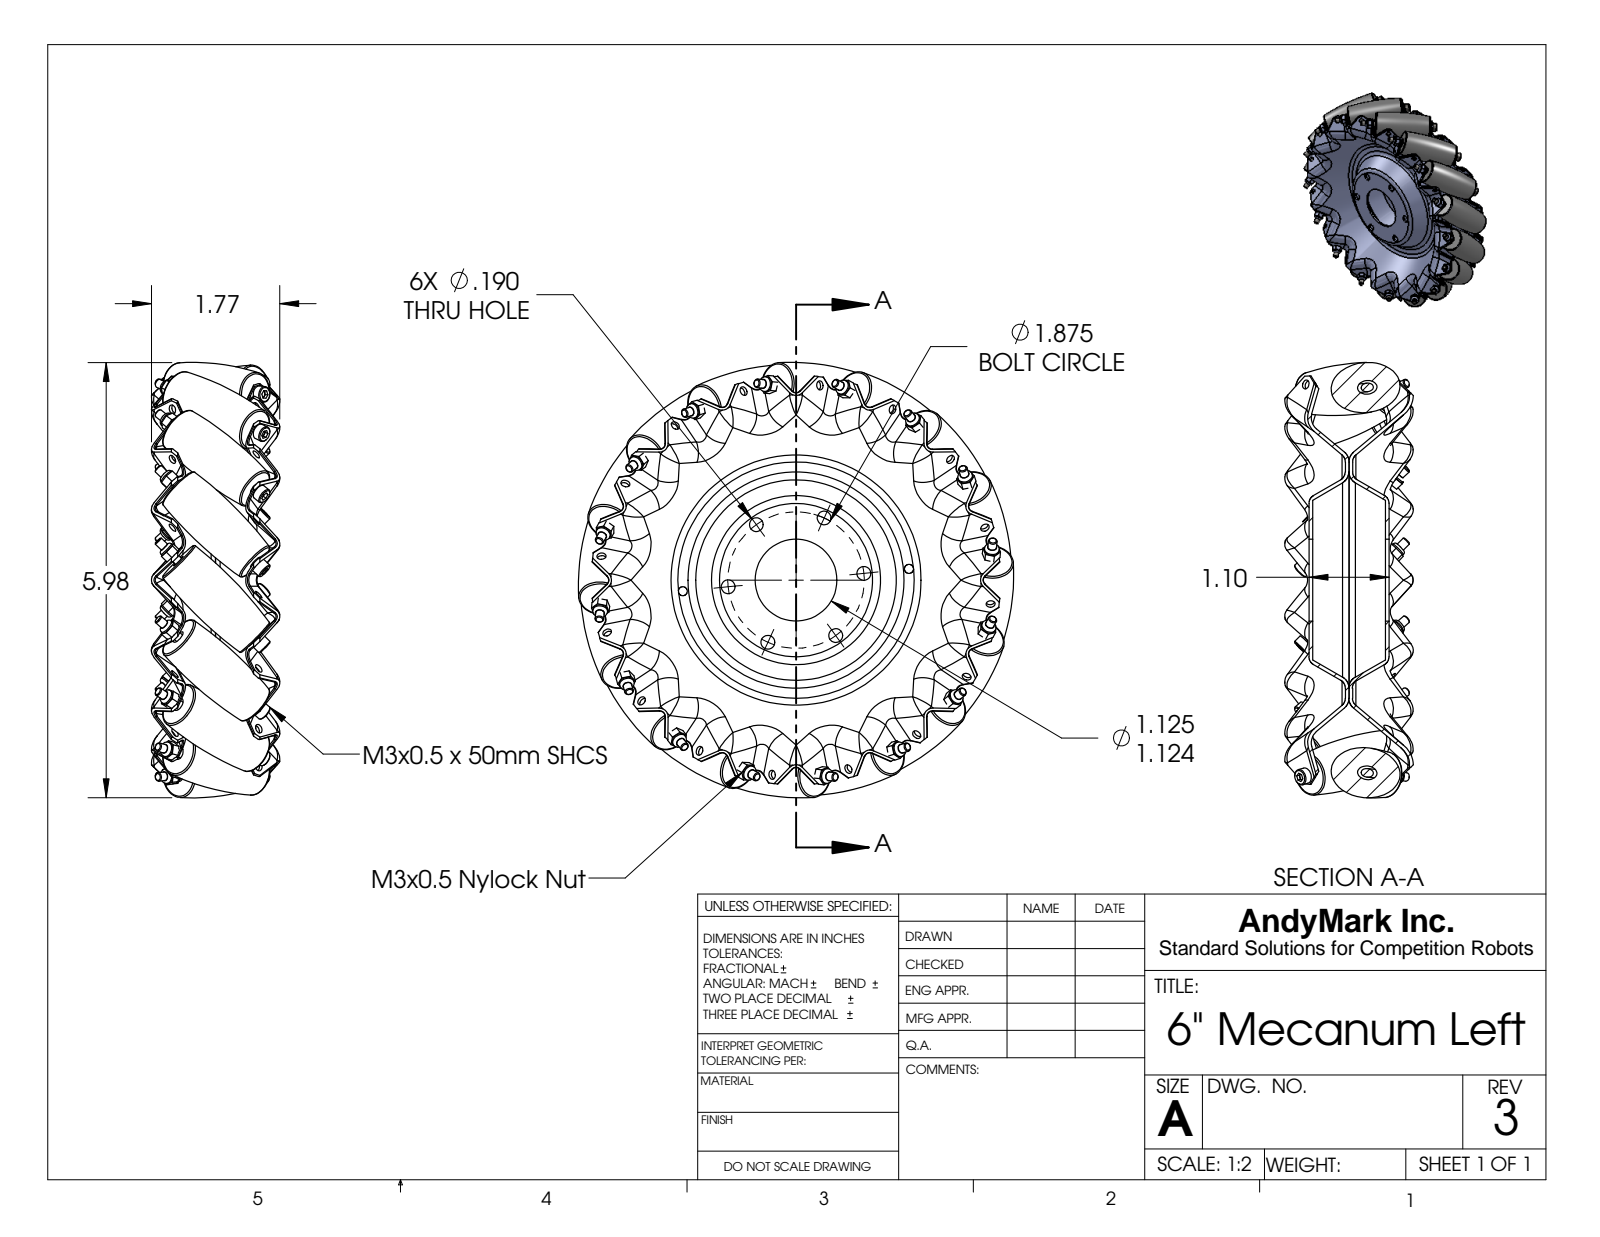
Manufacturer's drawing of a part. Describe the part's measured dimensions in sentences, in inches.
The part is named "1_6; 6-mecanum-3-Left; M3-Nylock-Nut_2; 6 mecanum plate 3 (+1 more)". Its 3-D file was written by "SolidWorks 2010 (CONFIG_CONTROL_DESIGN)". It is 50 solids with 1934 faces: 556 planar, 572 cylindrical and 806 other. Overall it measures 5.985 by 5.985 by 1.767 inches. Its volume is 11.1 cubic inches and its surface area 210.8 square inches. Round holes: 66 of diameter 0.125, 16 of diameter 0.118, 16 of diameter 0.187, 6 of diameter 0.19, 1 of diameter 1.125. Round bosses or shafts: 16 of diameter 0.217, 16 of diameter 0.205, 16 of diameter 0.118. Partial cylindrical surfaces (rounded edges, fillets, slot ends): 64 of radius 0.125, 32 of radius 0.075, 32 of radius 0.175, 1 of radius 2.813. The main face-to-face distances are 0.05, 0.5, 0.55, 1.05, 0.6, 0.45, 1, 1.1, 1.501, 1.569. The hole center spacings are 0.937, 0.938, 1.362, 1.624, 0.625, 1.624, 1.875, 2.187.
